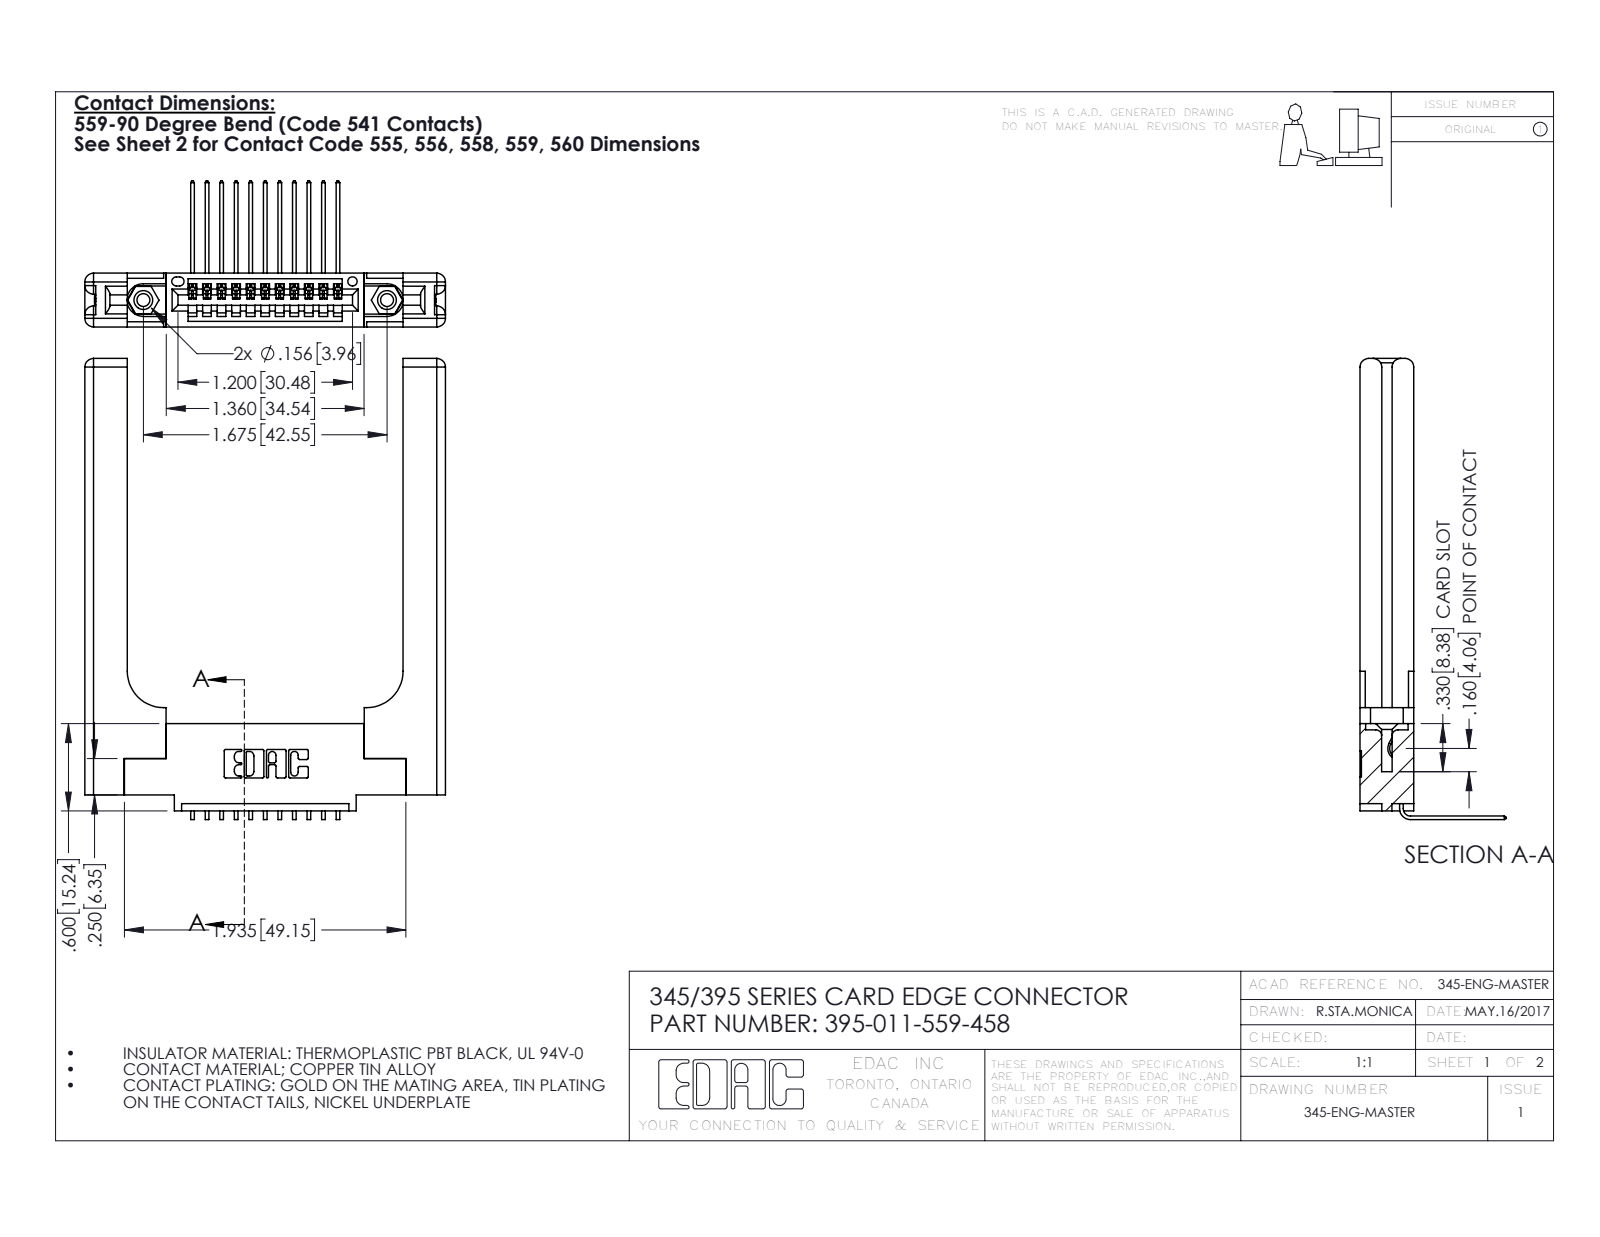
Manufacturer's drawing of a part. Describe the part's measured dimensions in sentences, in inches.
The part is named "345-220-058_345-220-058; 345-292-001_558 559 Tail - 1; 395-011-559-458; 345 Part_0.110 Offset - 0.156 Dia-TH (+1 more)". Its 3-D file was written by "SolidWorks 2016 (CONFIG_CONTROL_DESIGN)". It is 16 solids with 1046 faces: 694 planar, 292 cylindrical and 60 other. Overall it measures 3.169 by 2.479 by 1.005 inches. Its volume is 0.866 cubic inches and its surface area 19.75 square inches. Round holes: 2 of diameter 0.089, 2 of diameter 0.125, 2 of diameter 0.156, 1 of diameter 0.064. Round bosses or shafts: 2 of diameter 0.155. Partial cylindrical surfaces (rounded edges, fillets, slot ends): 22 of radius 0.006, 22 of radius 0.01, 16 of radius 0.06, 6 of radius 0.007, 6 of radius 0.031, 3 of radius 0.026, 2 of radius 0.03, 2 of radius 0.031. The main face-to-face distances are 0.37, 0.15, 0.072, 0.22, 0.148, 0.077, 0.298, 1.896, 0.071, 0.225. The hole center spacings are 0.27, 1.443, 1.675.
